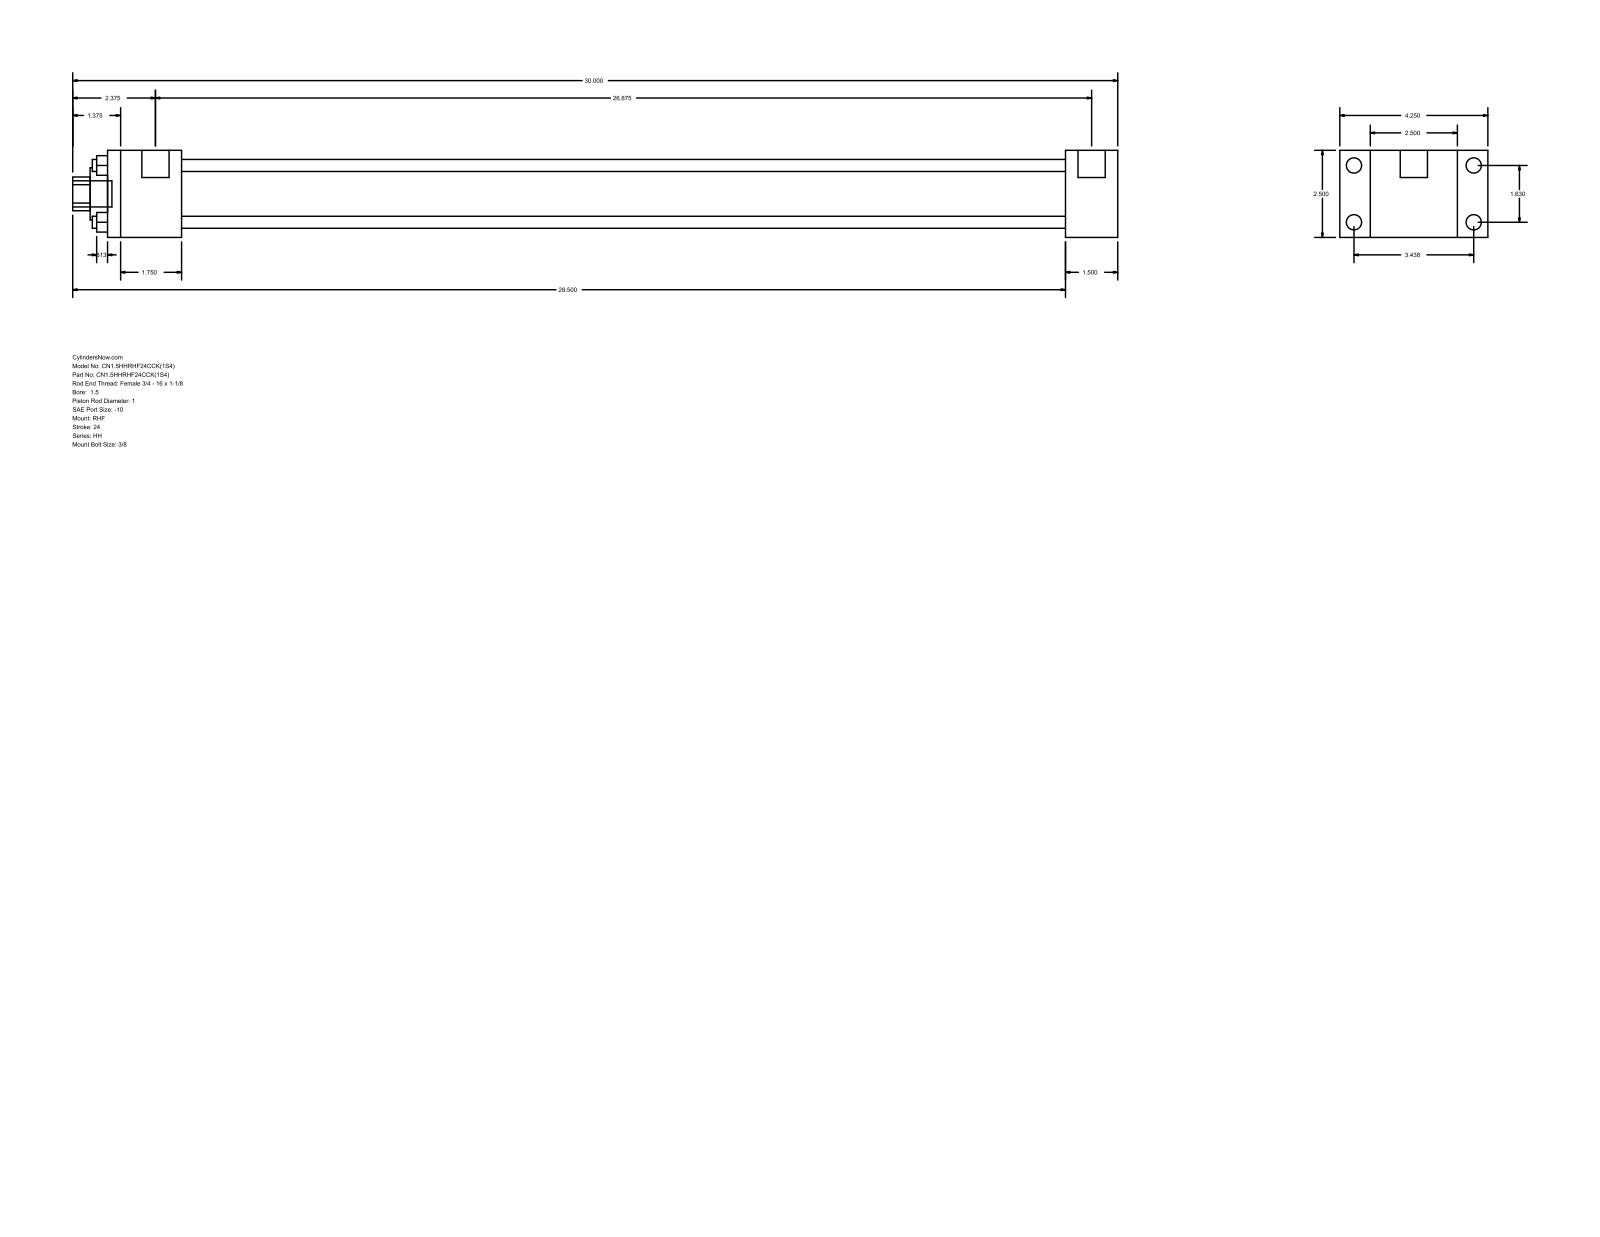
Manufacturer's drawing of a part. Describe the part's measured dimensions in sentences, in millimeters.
The part is named "HH_RHF__0150_1". Its 3-D file was written by "GSSL Pune (CONFIG_CONTROL_DESIGN)". It is 0 solids with 88 faces: 60 planar, 28 cylindrical and 0 other. Overall it measures 762 by 107.95 by 63.5 millimeters. Round holes: 4 of diameter 8.76, 1 of diameter 25.4, 1 of diameter 38.1, 1 of diameter 44.45. Round bosses or shafts: 4 of diameter 11.13, 4 of diameter 5.56, 2 of diameter 19.84, 1 of diameter 19.05. Partial cylindrical surfaces (rounded edges, fillets, slot ends): 1 of radius 12.29. The main face-to-face distances are 63.5, 22.23, 85.73, 38.1, 107.96, 644.52, 682.62, 53.98, 698.5, 736.6. The hole center spacings are 29.27, 41.4, 58.55.
